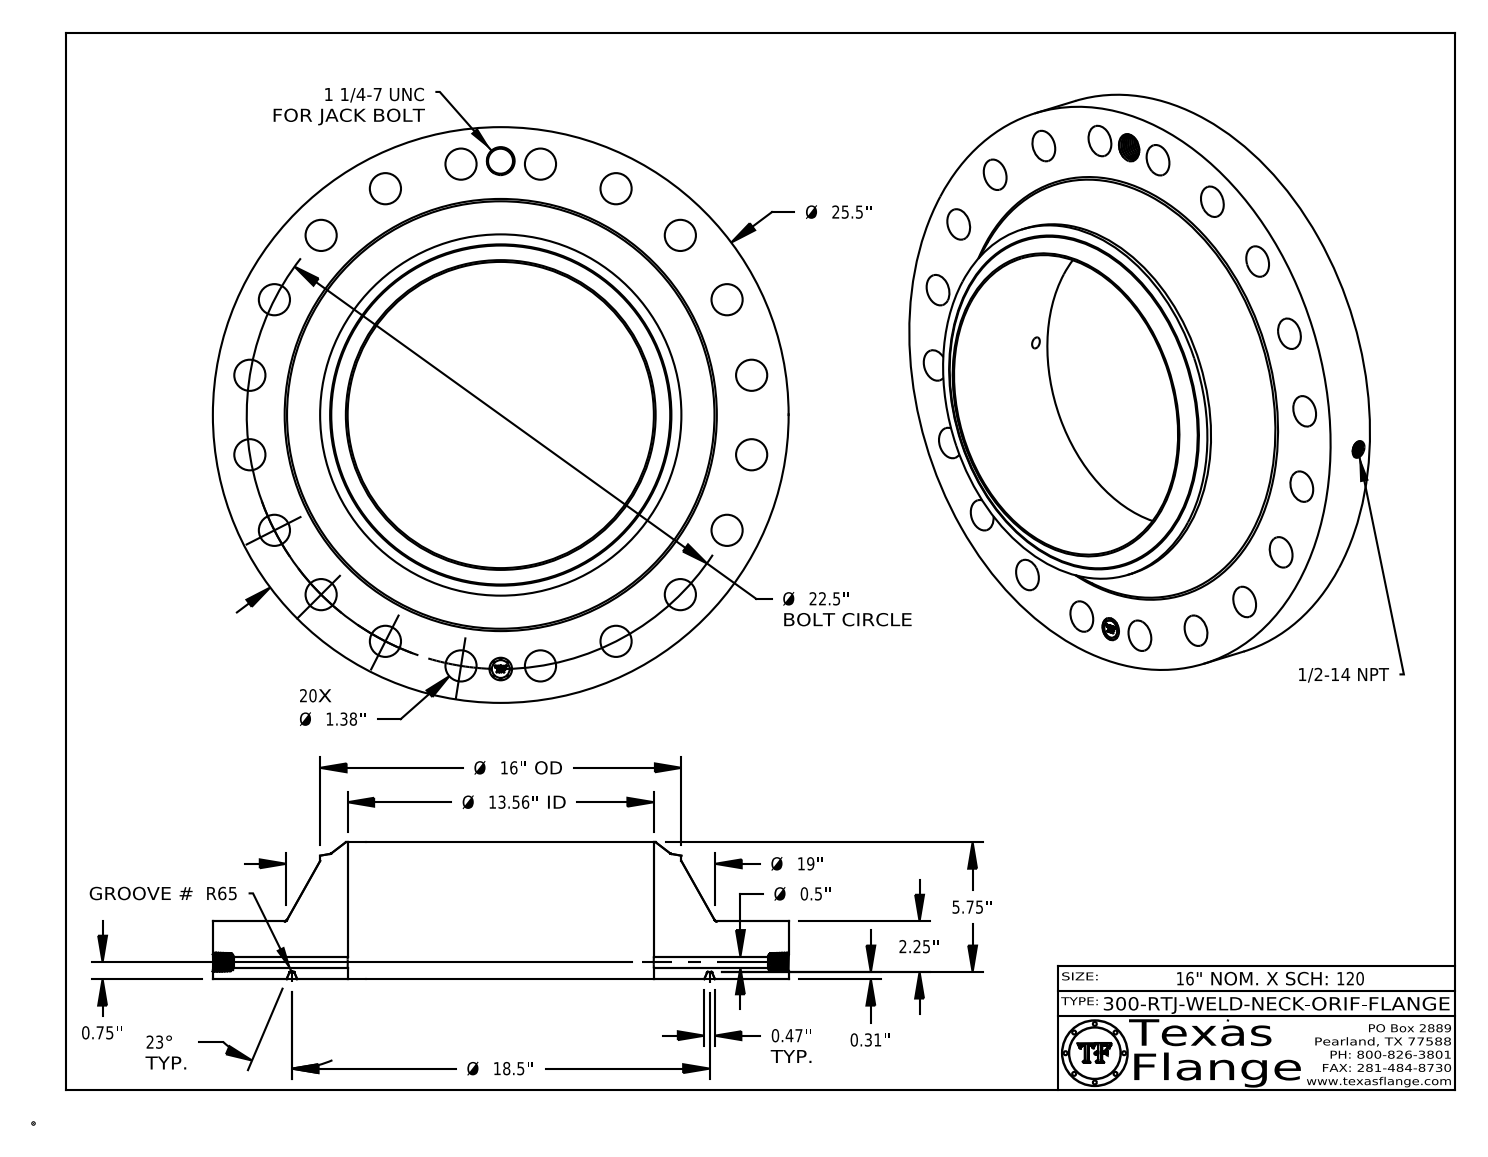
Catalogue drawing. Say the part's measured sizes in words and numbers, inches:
The part is named "300-RTJ-WELD-NECK". Its 3-D file was written by "CATIA V5 STEP AP214 (AUTOMOTIVE_DESIGN)". It is 1 solid with 823 faces: 370 planar, 121 cylindrical and 332 other. Overall it measures 25.5 by 25.5 by 6.063 inches. Its volume is 1 135 cubic inches and its surface area 1 520 square inches. Round holes: 20 of diameter 1.38, 1 of diameter 0.5, 1 of diameter 0.672, 1 of diameter 1, 1 of diameter 1.109, 1 of diameter 13.562. Round bosses or shafts: 8 of diameter 0.061, 1 of diameter 25.5, 1 of diameter 16, 1 of diameter 0.788. The main face-to-face distances are 2.563, 0.313, 2.25, 6.063, 5.75, 3.5, 2.548, 2.235, 0.015, 3.515. The hole center spacings are 3.52, 10.215, 18.203, 20.048, 21.399, 6.953, 11.25, 13.225.
